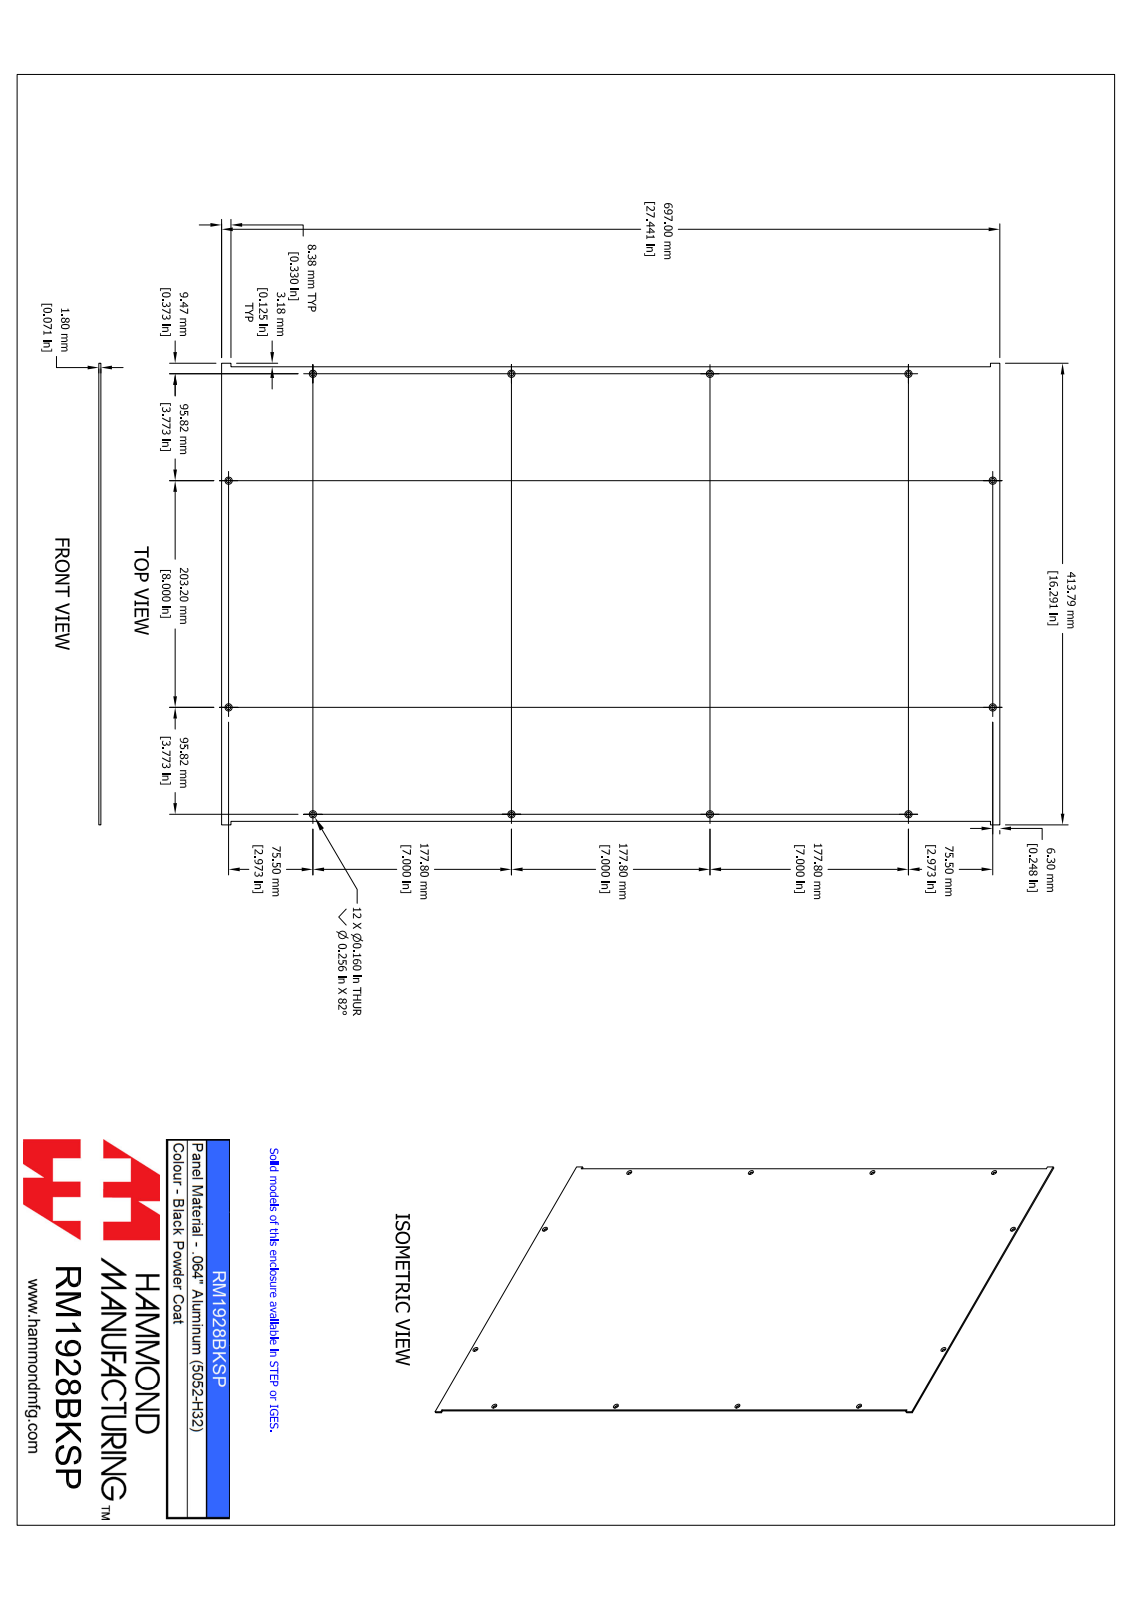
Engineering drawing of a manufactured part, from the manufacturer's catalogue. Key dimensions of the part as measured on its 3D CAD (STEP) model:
Part name (STEP PRODUCT): RM1928BKSP
STEP written by: SolidWorks 2021 (AUTOMOTIVE_DESIGN)
Units: inches
Bodies: 1 solid, 38 faces (14 planar, 12 cylindrical, 12 other)
Overall size (bounding box): 27.441 × 16.291 × 0.071
Volume: 31.24 in³ · Surface area: 886.7 in²
Round holes (diameter × count): ⌀0.16 ×12
Main face-to-face distances: 0.071, 16.041, 27.441, 0.125, 16.166, 16.291, 0.33, 27.111, 26.781
Hole centre spacings: 7, 17.048, 4.803, 10.662, 12.142, 14, 15.428, 15.545
